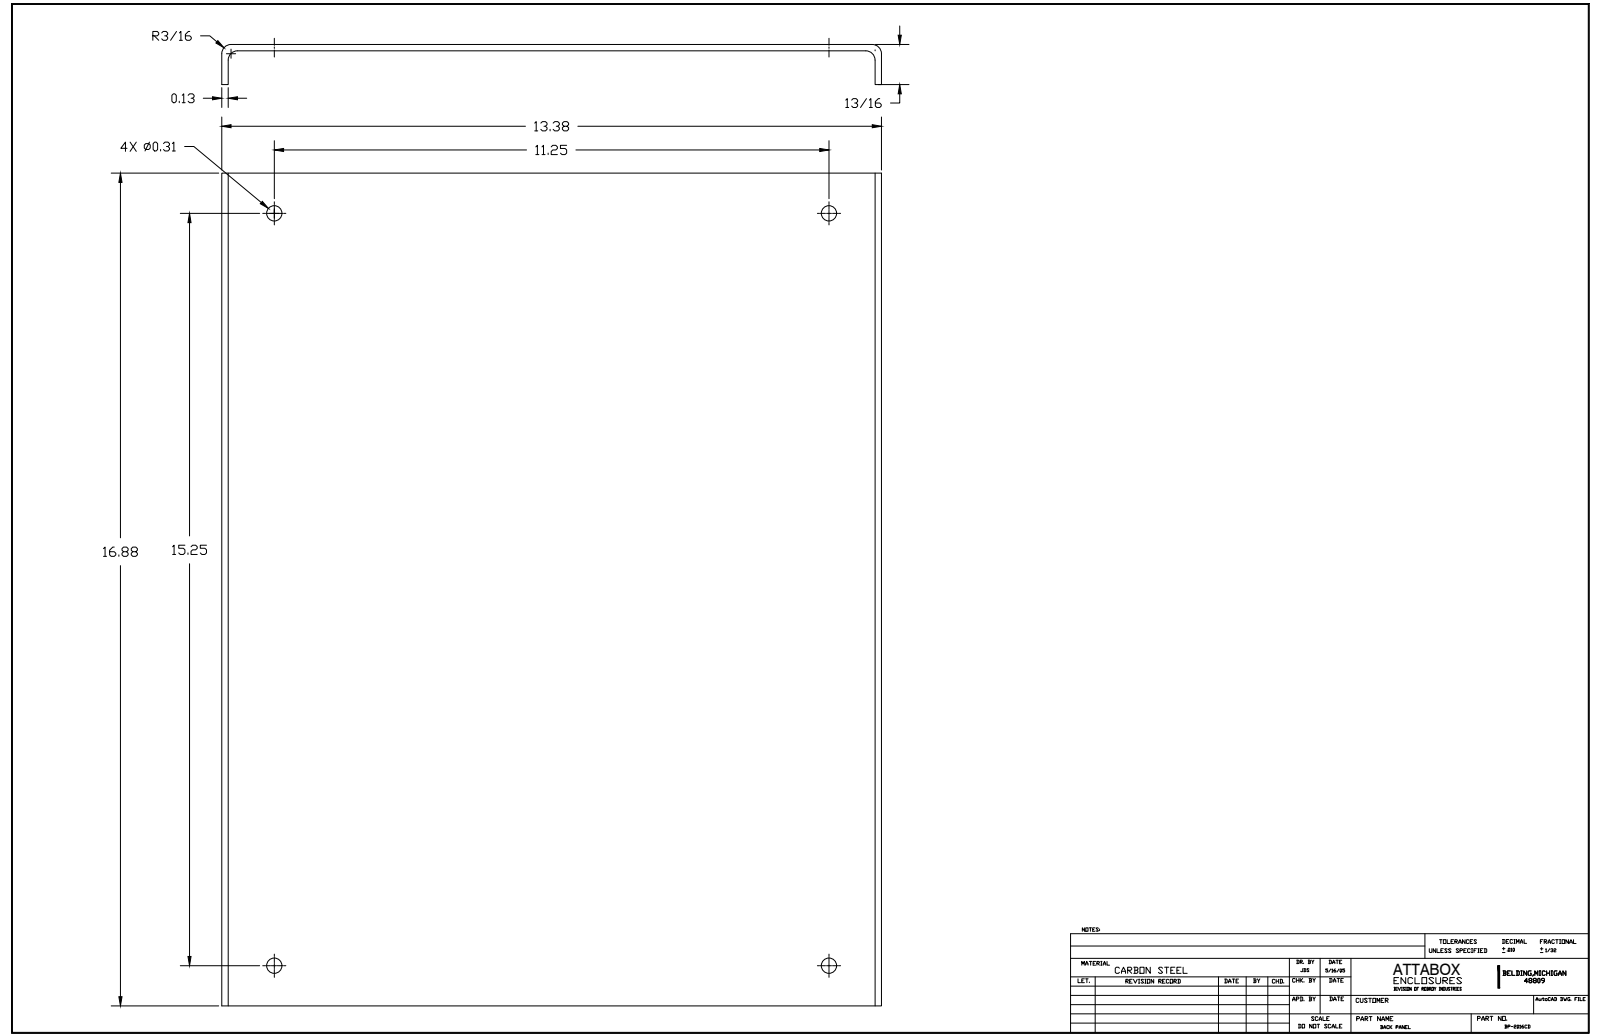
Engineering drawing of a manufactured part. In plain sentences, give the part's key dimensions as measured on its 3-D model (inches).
The part is named "BP2016CD". Its 3-D file was written by "SolidWorks 2018 (AUTOMOTIVE_DESIGN)". It is 1 solid with 18 faces: 10 planar, 8 cylindrical and 0 other. Overall it measures 16.875 by 13.375 by 0.5 inches. Its volume is 30.7 cubic inches and its surface area 480.7 square inches. Round holes: 4 of diameter 0.31. Partial cylindrical surfaces (rounded edges, fillets, slot ends): 2 of radius 0.188, 1 of radius 0.062, 1 of radius 0.063. The main face-to-face distances are 0.13, 13.245, 13.375, 13.115, 0.37, 0.5, 16.875. The hole center spacings are 11.25, 15.25, 18.951.
